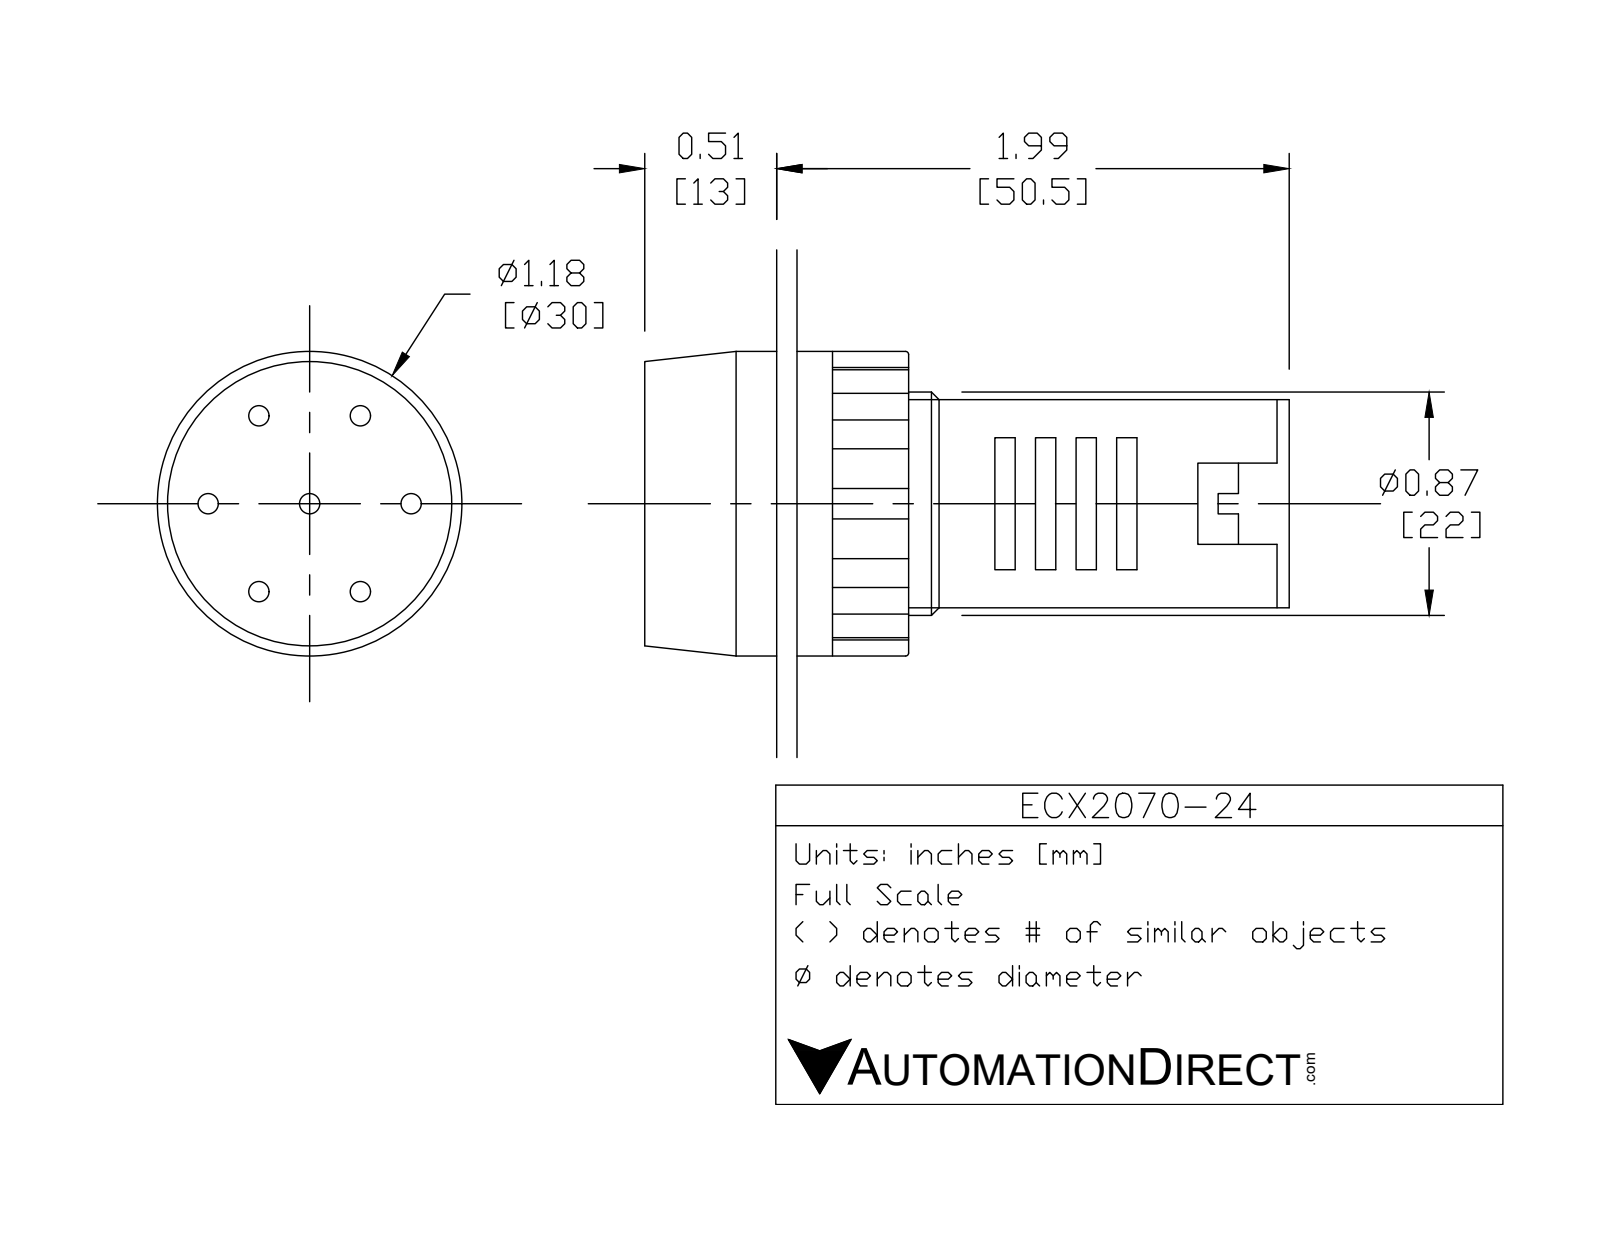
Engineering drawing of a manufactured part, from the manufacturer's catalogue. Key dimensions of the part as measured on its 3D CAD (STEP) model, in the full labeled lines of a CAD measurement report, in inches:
Part name (STEP PRODUCT): ECX2070-24
STEP written by: SolidWorks 2017 (AUTOMOTIVE_DESIGN)
Units: inches
Bodies: 6 solids, 196 faces (89 planar, 79 cylindrical, 28 other)
Overall size (bounding box): 2.5 × 1.181 × 1.181
Volume: 1.602 in³ · Surface area: 19.2 in²
Round holes (diameter × count): ⌀0.079 ×4, ⌀0.217 ×2, ⌀0.866 ×1, ⌀0.886 ×1
Round bosses / shafts (diameter × count): ⌀0.157 ×2, ⌀1.181 ×1, ⌀1.142 ×1, ⌀1.043 ×1, ⌀0.787 ×1
Partial cylindrical surfaces — rounded edges, fillets, slot ends (radius × count): R0.01 ×22, R0.039 ×8, R0.354 ×1
Main face-to-face distances: 0.079, 0.157, 0.236, 0.315, 0.394, 0.472, 0.492, 0.63, 0.02, 0.512
Hole centre spacings: 0.294, 0.394, 0.538, 0.557, 0.182, 0.787, 0.364
